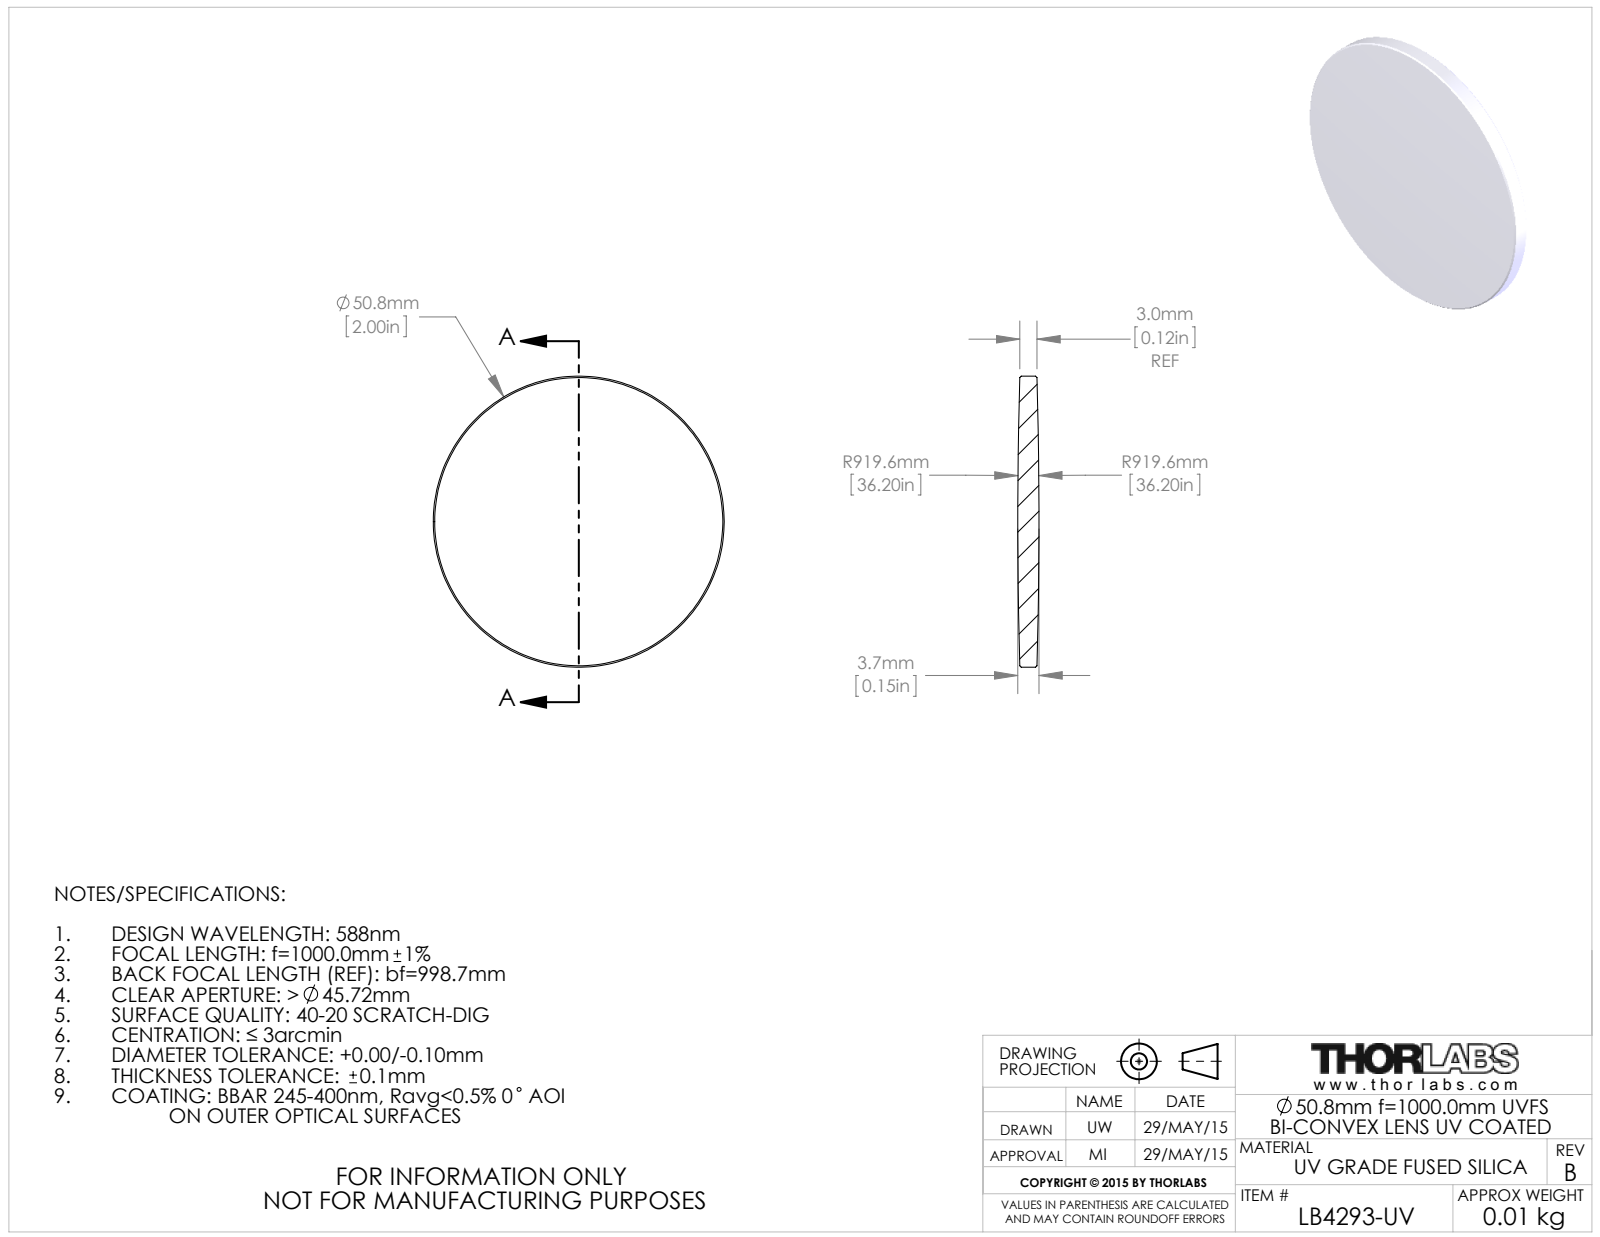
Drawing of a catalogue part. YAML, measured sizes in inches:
part_name: "4340-E0W"
step_written_by: "SolidWorks 2014 (CONFIG_CONTROL_DESIGN)"
units: inches
bodies: {solids: 1, faces: 10, planar: 0, cylindrical: 2, other: 8}
overall_size: [2, 2, 0.146]
volume: 0.414
surface_area: 6.956
round_bosses_or_shafts:
  - {diameter: 2, count: 1}
